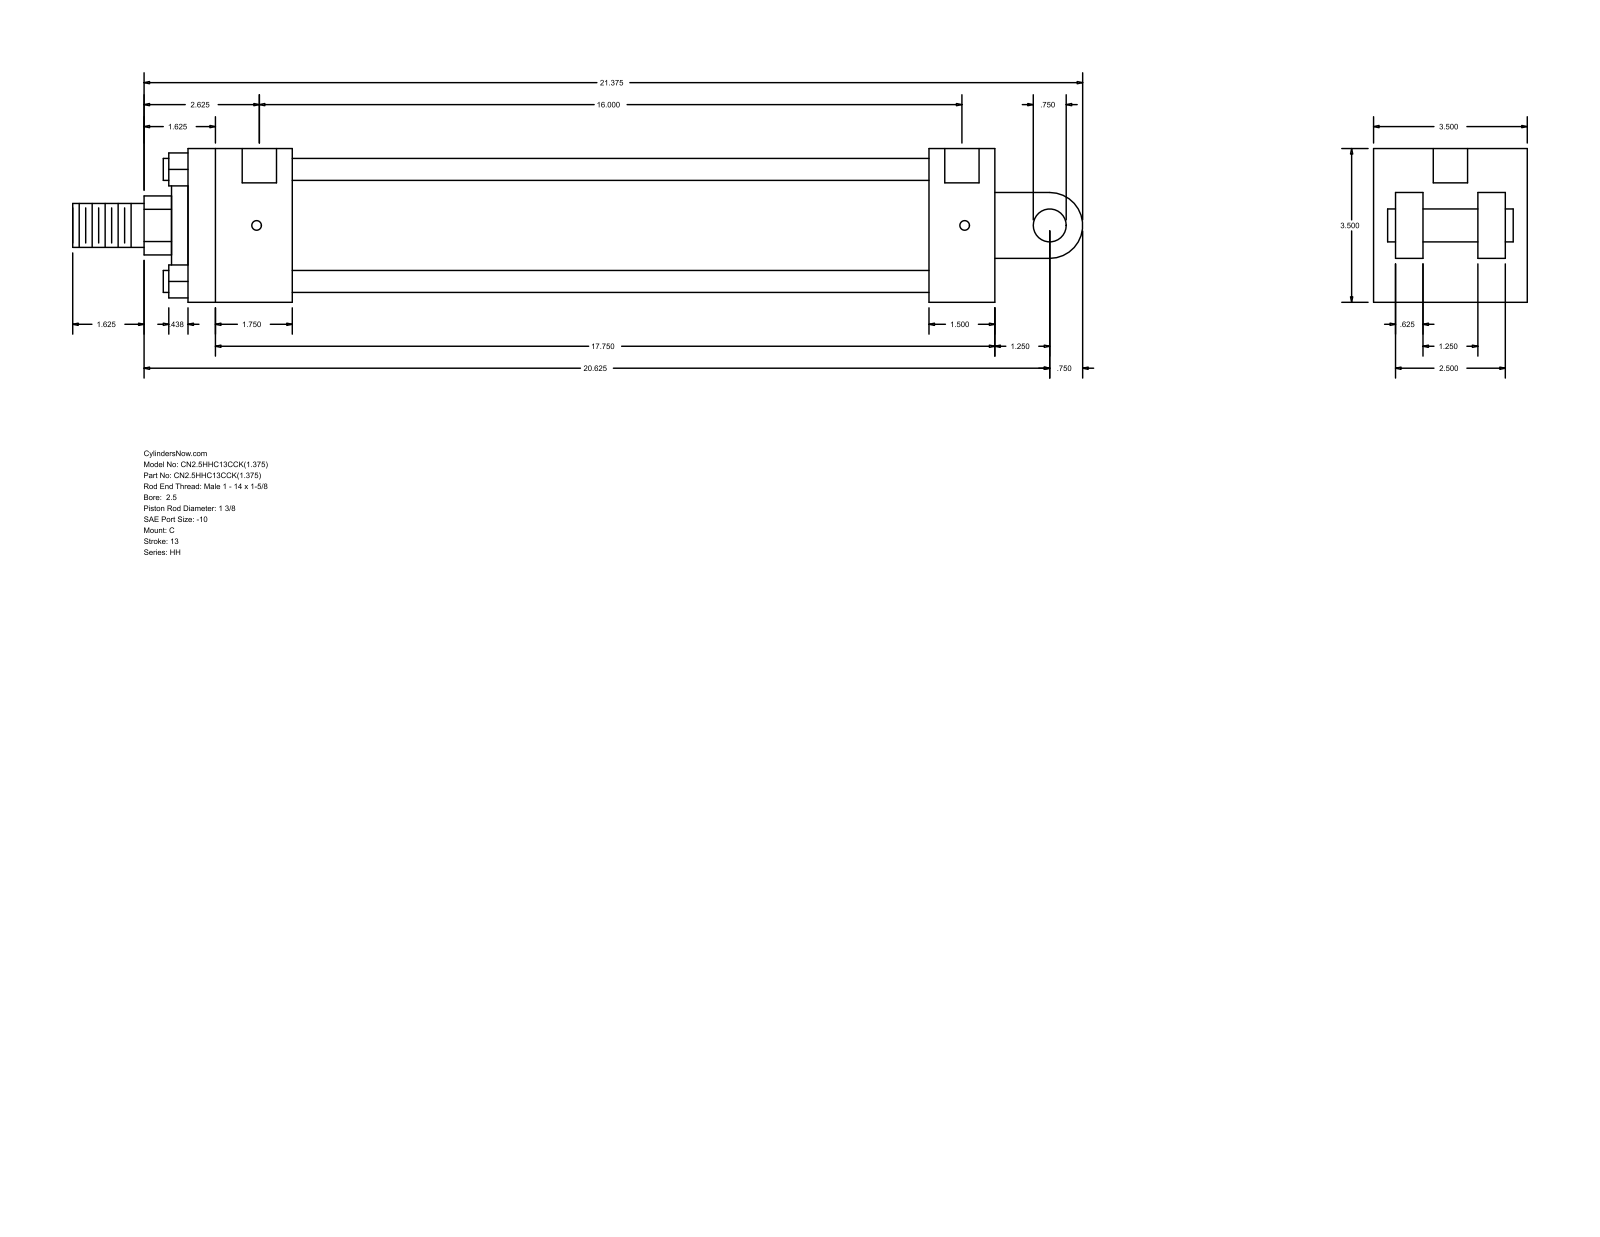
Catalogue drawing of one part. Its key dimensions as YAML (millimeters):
part_name: "HH_C__0250_1.375"
step_written_by: "GSSL Pune (CONFIG_CONTROL_DESIGN)"
units: millimeters
bodies: {solids: 0, faces: 99, planar: 70, cylindrical: 29, other: 0}
overall_size: [584.2, 88.9, 88.9]
round_holes:
  - {diameter: 5.56, count: 4}
  - {diameter: 19.84, count: 2}
round_bosses_or_shafts:
  - {diameter: 12.7, count: 4}
  - {diameter: 73.03, count: 1}
  - {diameter: 50.8, count: 1}
  - {diameter: 34.92, count: 1}
  - {diameter: 25.4, count: 1}
  - {diameter: 19.05, count: 1}
partial_cylinders:
  - {radius: 17.06, count: 1}
  - {radius: 19.05, count: 1}
face_to_face_distances: [88.9, 466.72, 38.1, 63.5, 12.7, 428.62, 60.32, 368.3, 406.4, 76.2]
hole_center_spacings: [409.57, 1.58, 1.59, 406.4, 407.98, 407.99]
